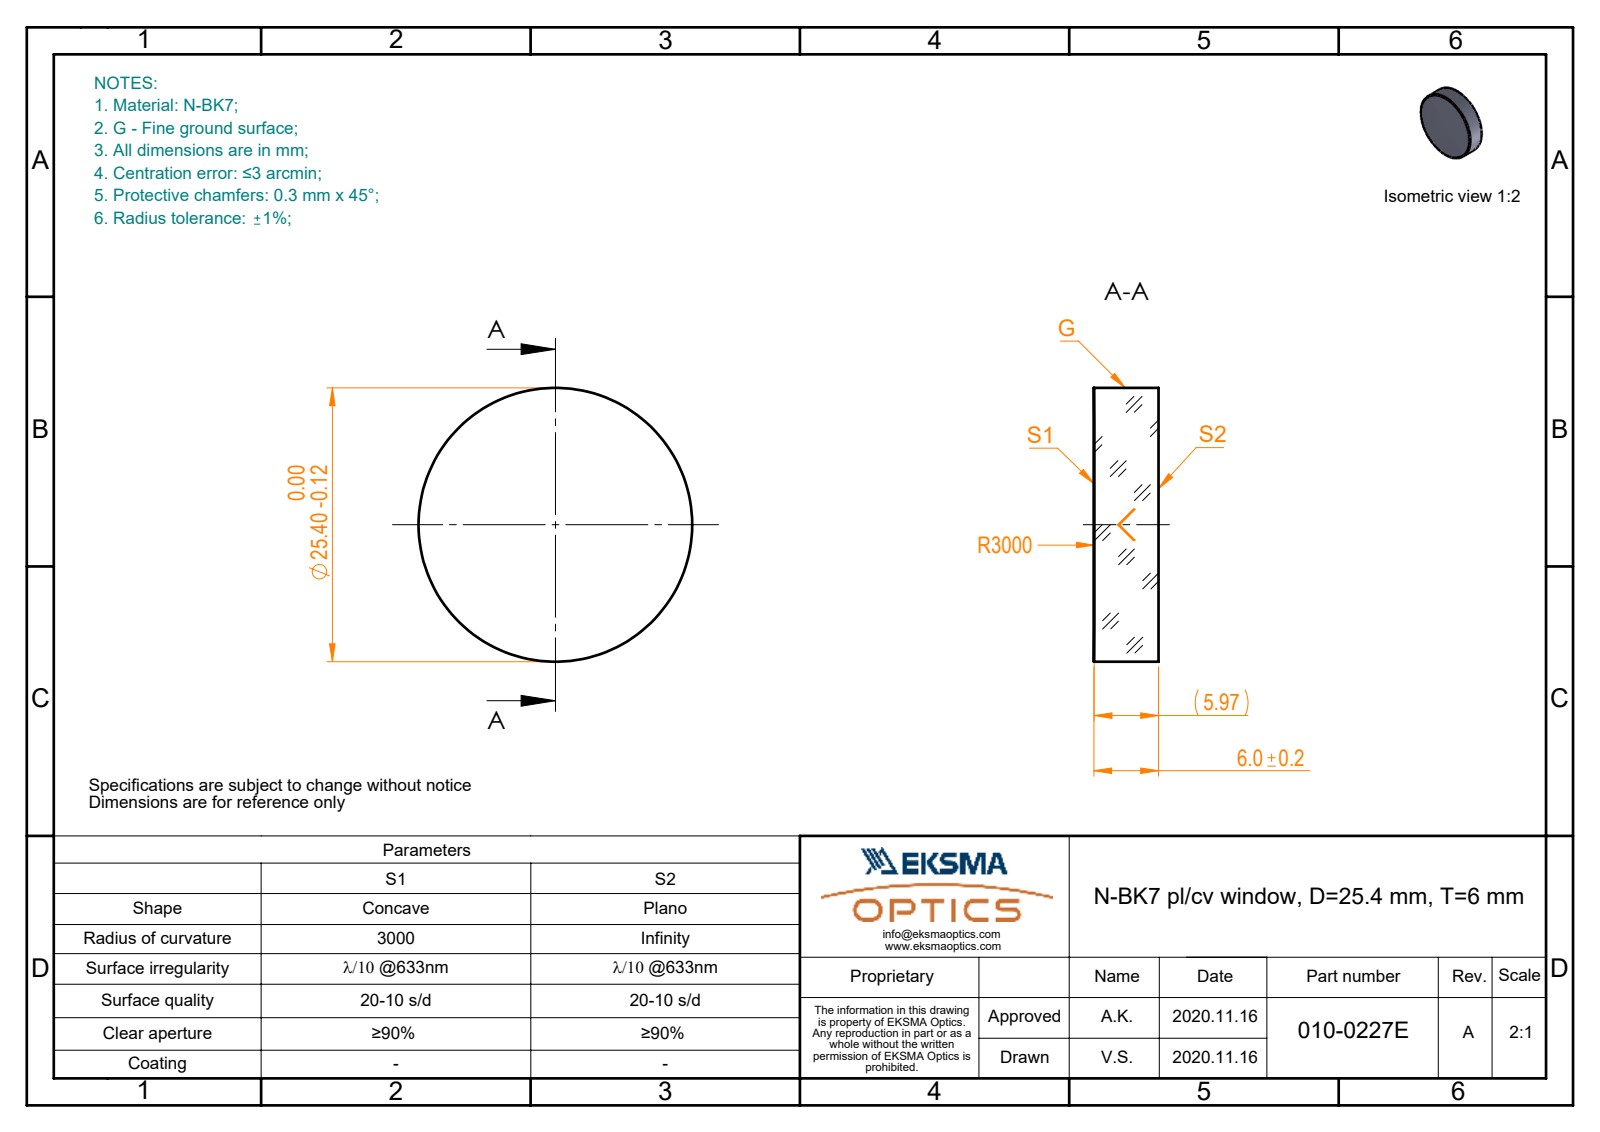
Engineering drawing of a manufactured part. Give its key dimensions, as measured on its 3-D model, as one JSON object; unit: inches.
{"part_name": "010-0227E_N-BK7_PCV_window", "step_written_by": "SolidWorks 2019 (CONFIG_CONTROL_DESIGN)", "units": "inches", "bodies": {"solids": 1, "faces": 5, "planar": 1, "cylindrical": 2, "other": 2}, "overall_size": [1, 1, 0.236], "volume_in3": 0.185, "surface_area_in2": 2.313, "round_bosses_or_shafts": [[1, 1]]}
